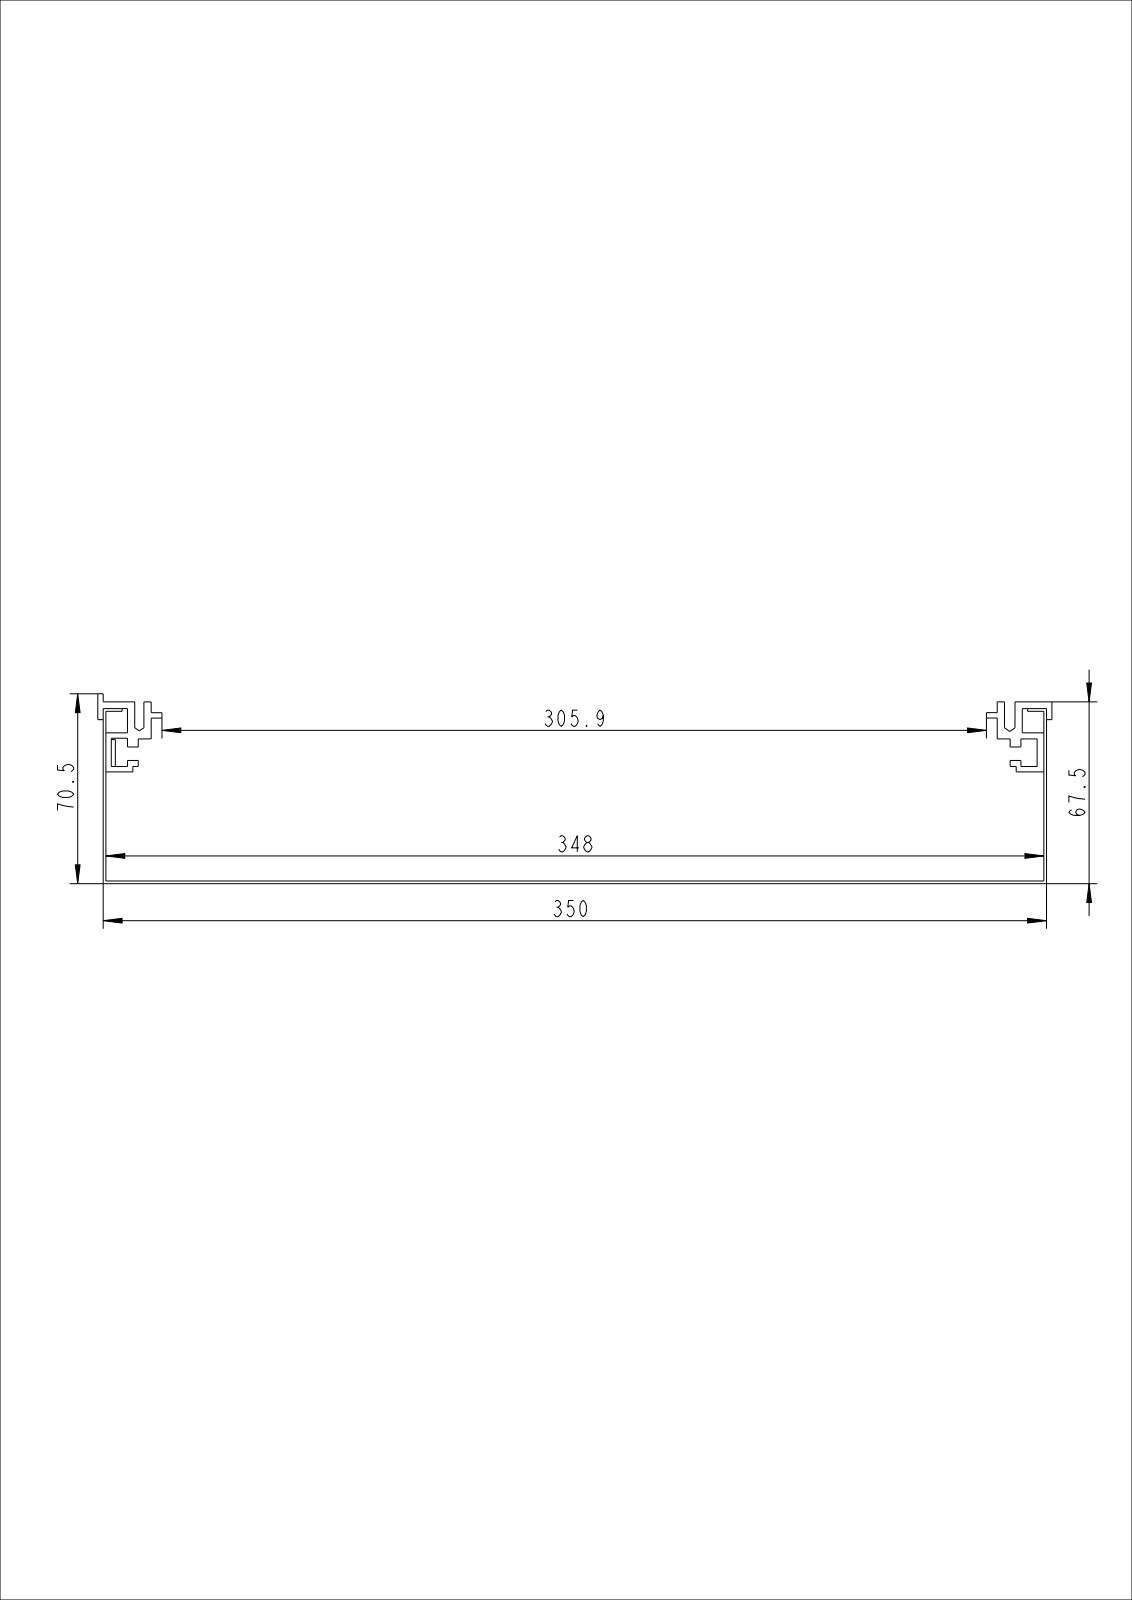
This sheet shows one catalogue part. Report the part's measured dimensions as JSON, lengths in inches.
{"part_name": "AKU3500701_WANNE_3; AKU_SEITENPROFIL_APA_K24_6; ZES_VK180_KUN_3; AKU_SEITENPROFIL_APA_O01_4 (+2 more)", "step_written_by": "CREO PARAMETRIC BY PTC INC, 2022281 (AUTOMOTIVE_DESIGN)", "units": "inches", "bodies": {"solids": 9, "faces": 265, "planar": 253, "cylindrical": 12, "other": 0}, "overall_size": [96.457, 13.937, 2.776], "volume_in3": 111.1, "surface_area_in2": 4498, "round_holes": [[0.217, 4], [0.165, 2]], "face_to_face_distances": [0.039, 13.74, 13.701, 13.78, 0.079, 2.52, 0.315, 0.118, 0.354, 2.559], "hole_center_spacings": [0.364, 2.618, 0.728, 2.254, 2.982, 1.89, 3.346]}
